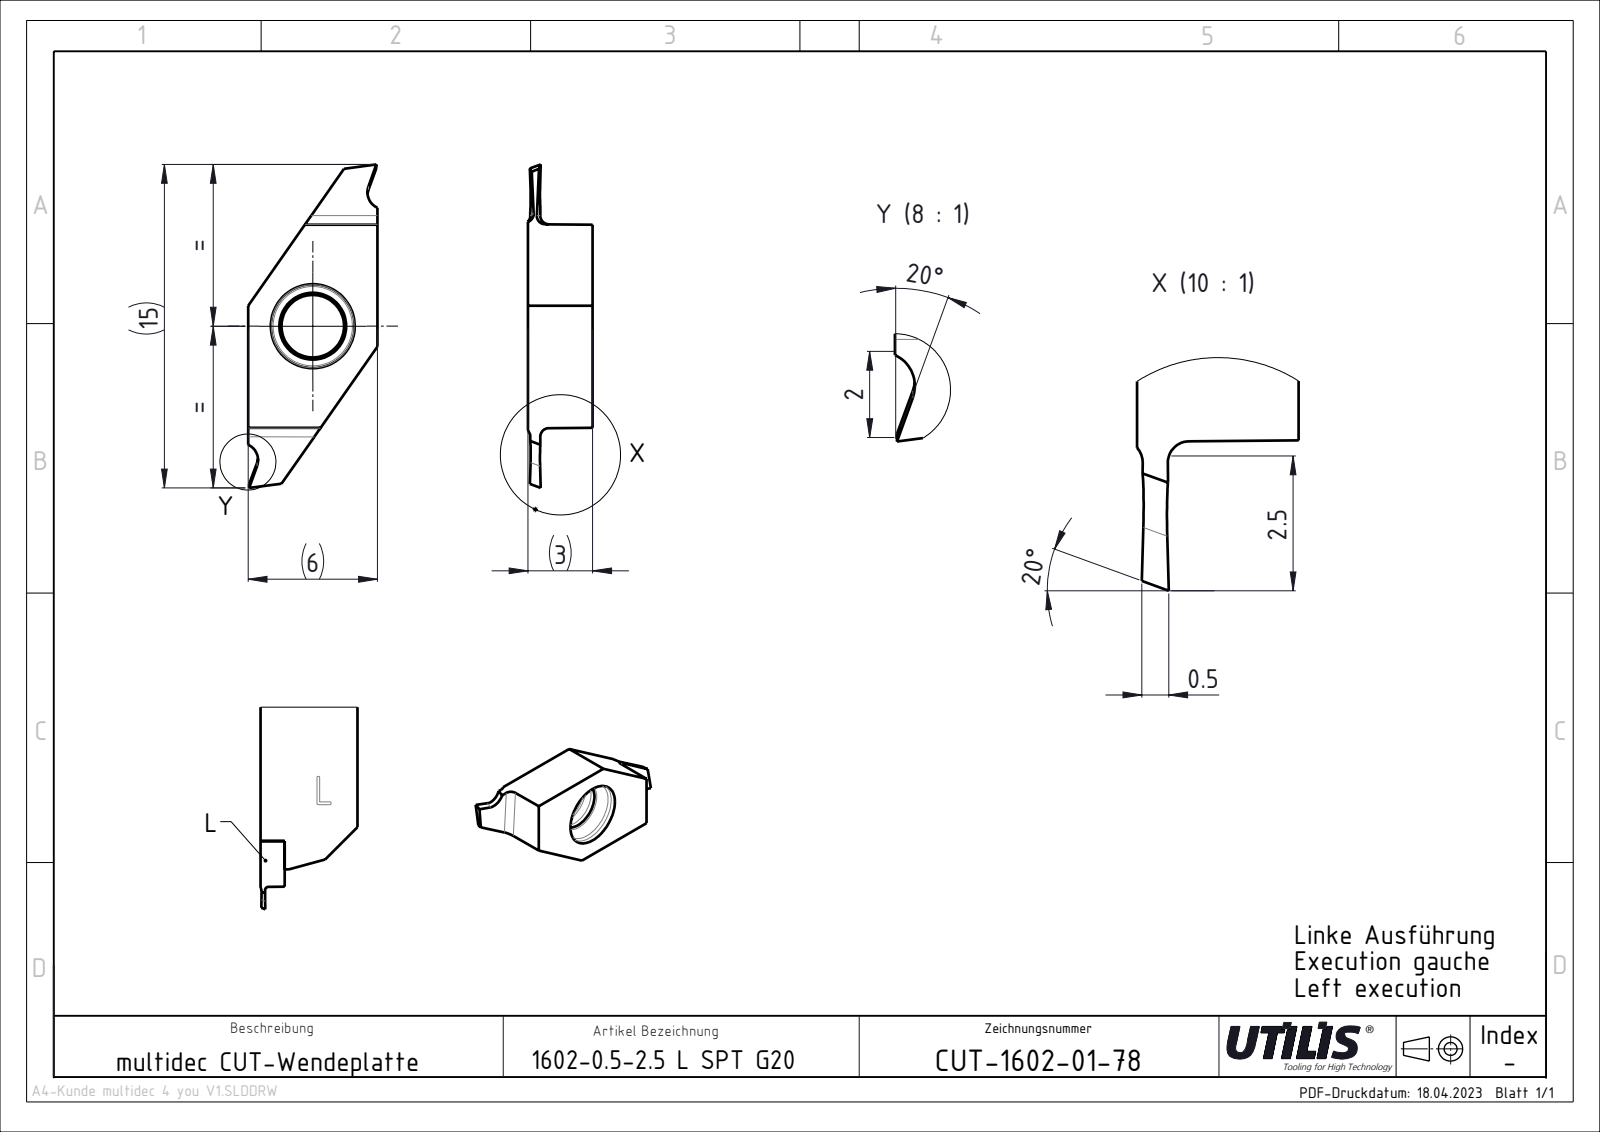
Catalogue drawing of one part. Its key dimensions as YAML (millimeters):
part_name: "1-CUT-1602-01-78 stp"
step_written_by: "SolidWorks 2022 (AUTOMOTIVE_DESIGN)"
units: millimeters
bodies: {solids: 1, faces: 19, planar: 14, cylindrical: 5, other: 0}
overall_size: [15, 6, 3]
volume: 127
surface_area: 218
round_holes:
  - {diameter: 2.9, count: 1}
partial_cylinders:
  - {radius: 0.4, count: 4}
face_to_face_distances: [3, 6, 0.36]
